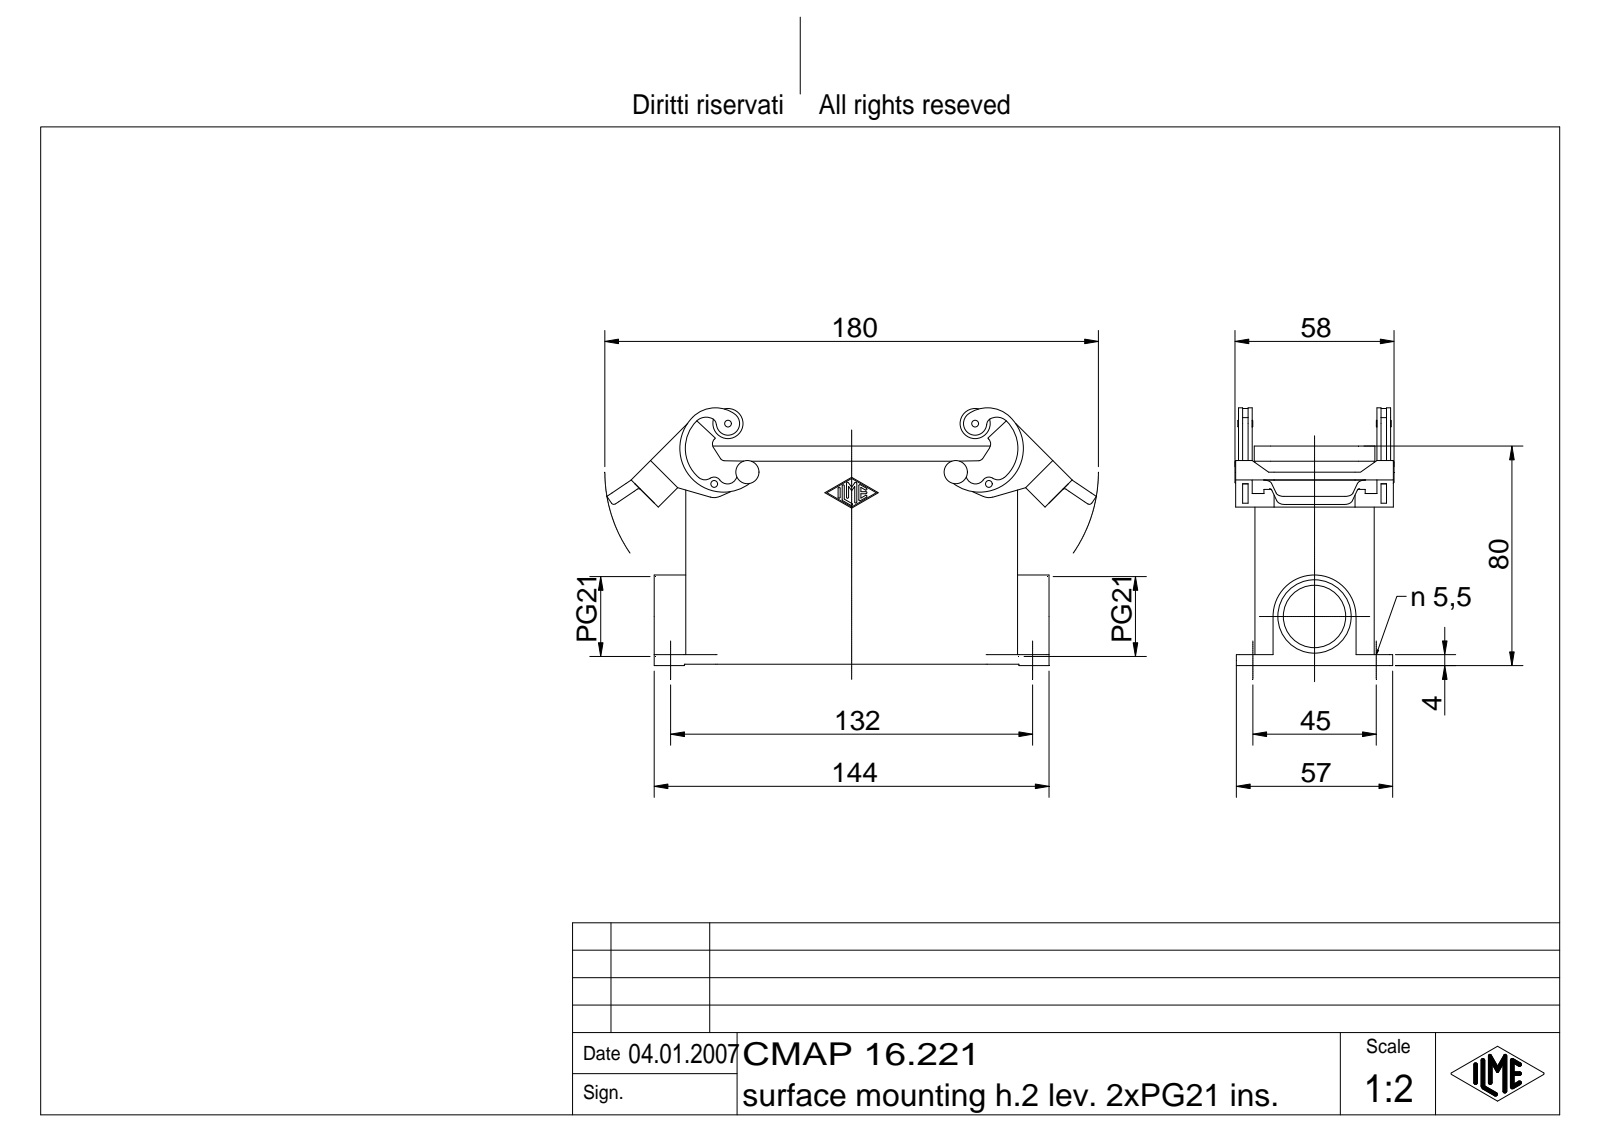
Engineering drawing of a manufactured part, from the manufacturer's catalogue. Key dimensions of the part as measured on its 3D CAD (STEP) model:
Part name (STEP PRODUCT): CMAP 16.221
STEP written by: Autodesk Inventor 7 (AUTOMOTIVE_DESIGN)
Units: millimetres
Bodies: 1 solid, 748 faces (191 planar, 205 cylindrical, 352 other)
Overall size (bounding box): 178.49 × 93.94 × 58
Volume: 144 768 mm³ · Surface area: 80 756 mm²
Round holes (diameter × count): ⌀2 ×4, ⌀5.5 ×4, ⌀2.5 ×2, ⌀22.78 ×1, ⌀26.78 ×1
Round bosses / shafts (diameter × count): ⌀11 ×2, ⌀5 ×2, ⌀3 ×2
Partial cylindrical surfaces — rounded edges, fillets, slot ends (radius × count): R1 ×20, R0.38 ×14, R3 ×12, R6 ×8, R2.5 ×6, R1.5 ×4, R2 ×4, R3.5 ×4
Main face-to-face distances: 3, 40.5, 43.5, 37.5, 3.5, 4, 0.75, 50.5, 40.75, 3.75
Hole centre spacings: 22.56, 45, 97.67, 132, 139.46, 90.14, 100.18
